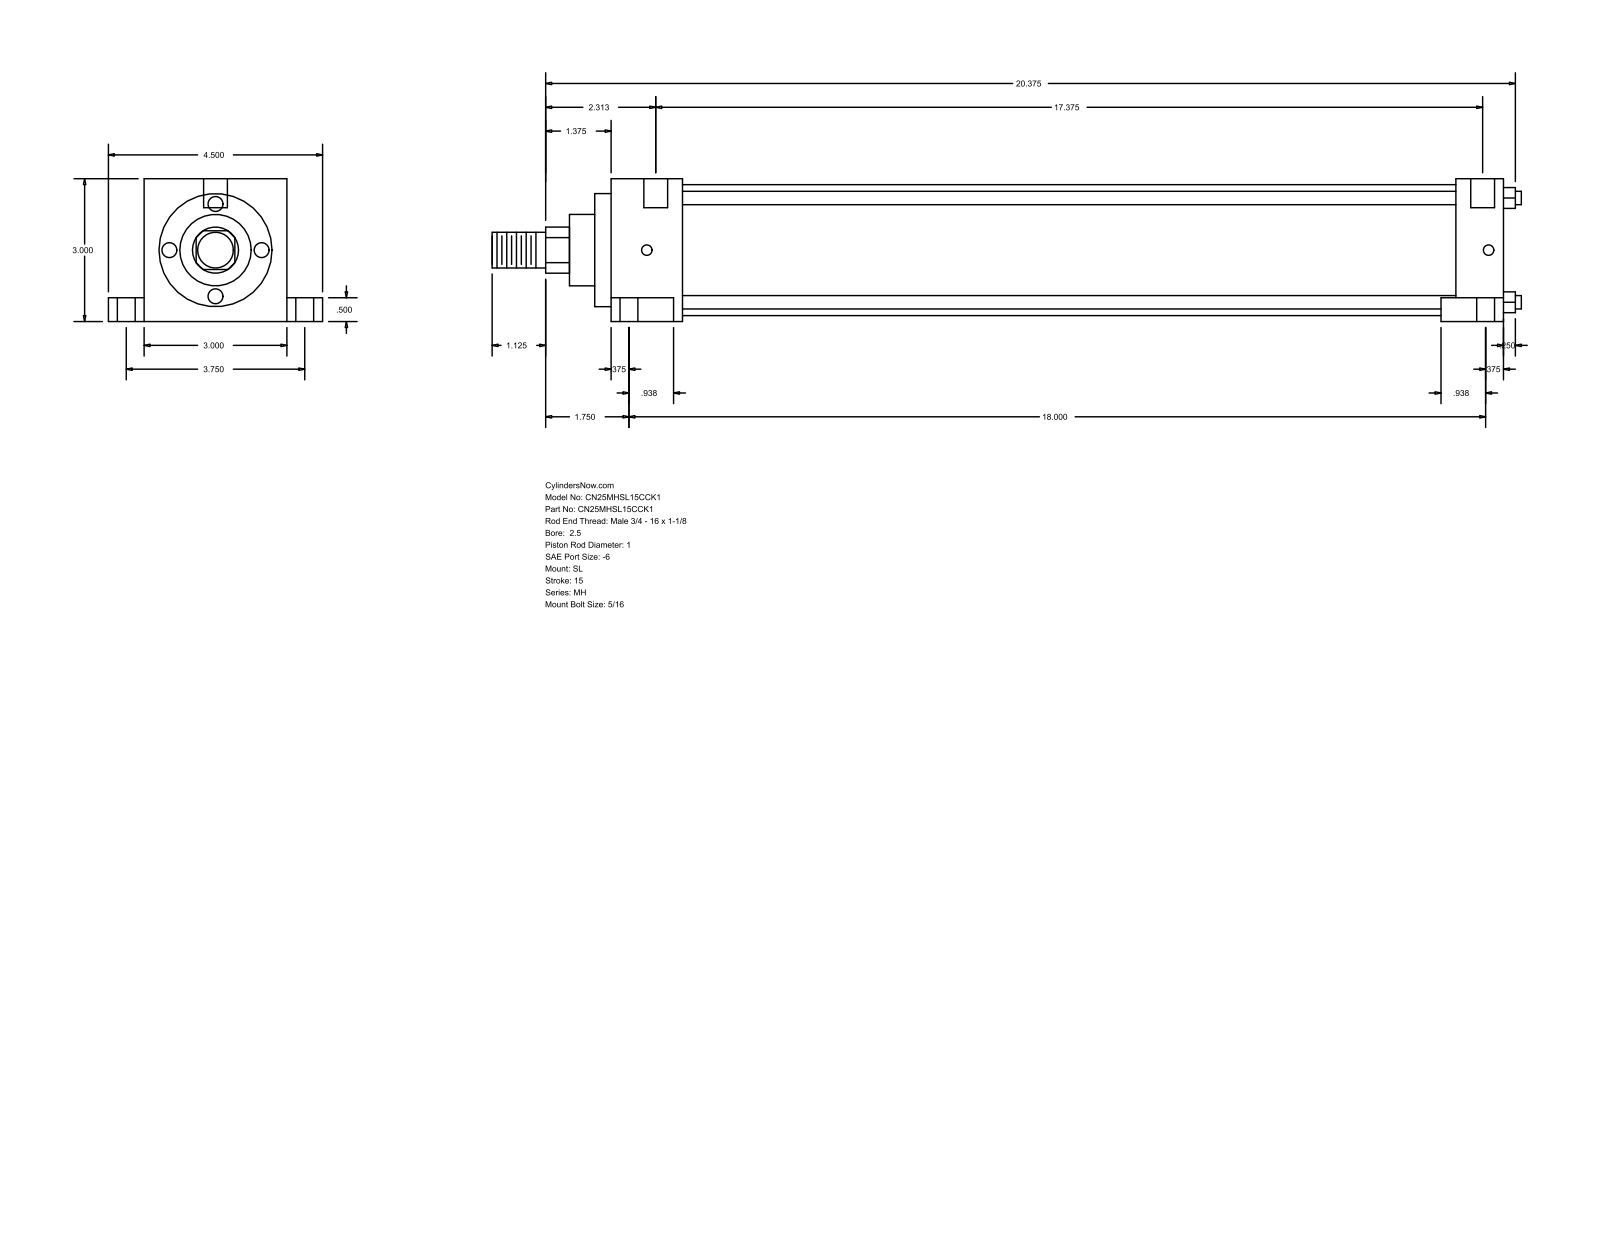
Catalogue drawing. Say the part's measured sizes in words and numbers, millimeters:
The part is named "MH_SL__0250_1". Its 3-D file was written by "GSSL Pune (CONFIG_CONTROL_DESIGN)". It is 0 solids with 86 faces: 61 planar, 25 cylindrical and 0 other. Overall it measures 549.27 by 114.3 by 76.2 millimeters. Round holes: 2 of diameter 5.56, 2 of diameter 9.53, 2 of diameter 15.88, 1 of diameter 12.7. Round bosses or shafts: 4 of diameter 7.14, 1 of diameter 69.85, 1 of diameter 60.33, 1 of diameter 38.1, 1 of diameter 25.4, 1 of diameter 19.05. Partial cylindrical surfaces (rounded edges, fillets, slot ends): 1 of radius 12.29. The main face-to-face distances are 76.2, 25.41, 459.58, 484.99, 12.7, 63.5, 19.05, 95.25, 13.49, 473.07. The hole center spacings are 47.65, 3.18, 95.24.
